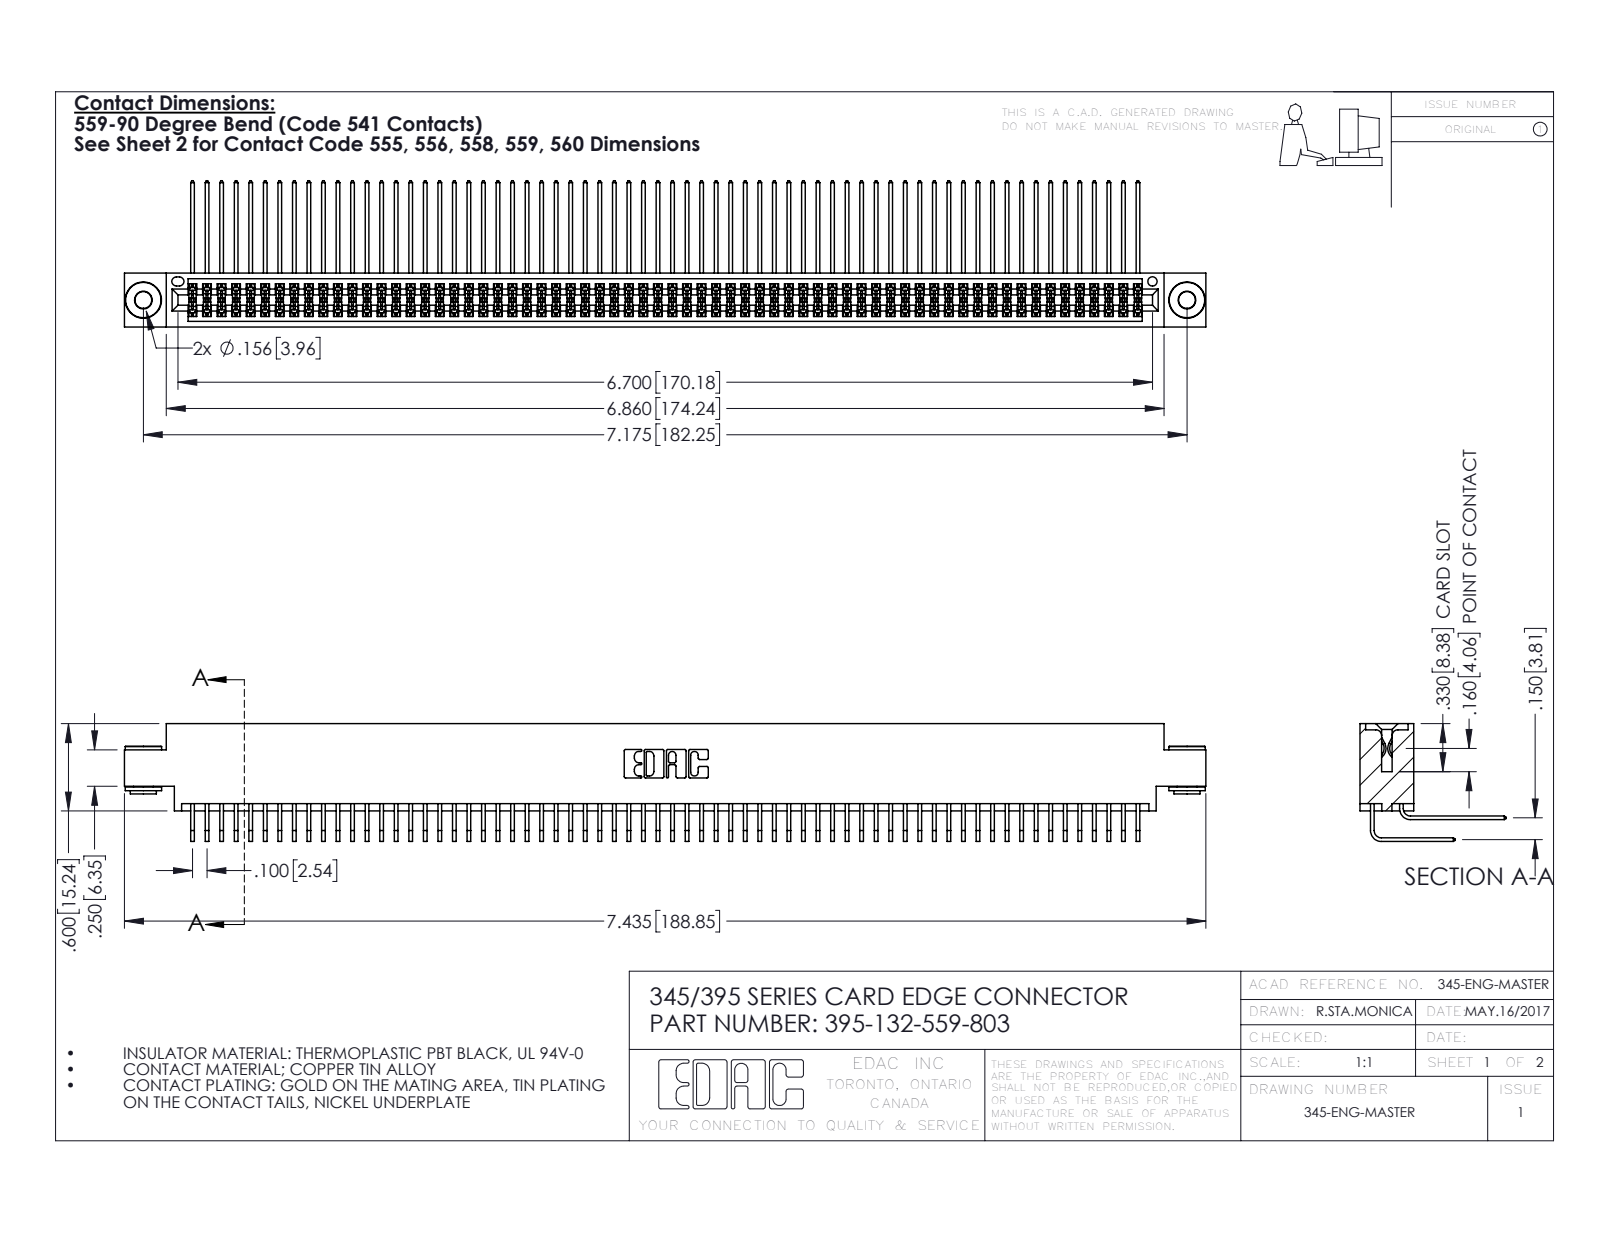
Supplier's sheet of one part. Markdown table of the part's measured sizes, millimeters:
| quantity | value |
| --- | --- |
| part name | 345-292-001_559 Tail - 2; 395-132-559-803; 345-250-002_345-250-002-102; 345 Part_0.170 Offset - 0.156 Dia-TH (+1 more) |
| STEP written by | SolidWorks 2016 (CONFIG_CONTROL_DESIGN) |
| units | millimeters |
| bodies | 135 solids, 7032 faces (4714 planar, 2310 cylindrical, 8 other) |
| overall size | 188.8 × 25.5 × 20.5 |
| volume | 19 240 mm³ |
| surface area | 32 830 mm² |
| round holes (diameter × count) | 2.9 × 2, 4 × 2, 1.6 × 1 |
| round bosses / shafts (diameter × count) | 6.4 × 2, 4.6 × 2, 3.5 × 2 |
| partial cylindrical surfaces (radius × count) | 0.2 × 198, 0.3 × 22, 0.2 × 6, 0.8 × 6, 0.7 × 3, 0.4 × 2, 0.5 × 2, 0.6 × 2 |
| main face-to-face distances | 1.8, 7.6, 9.4, 5.1, 2.5, 6.9, 0.6, 5.7, 4.4, 3.8 |
| hole center spacings | 6.9, 176.3, 182.2 |
